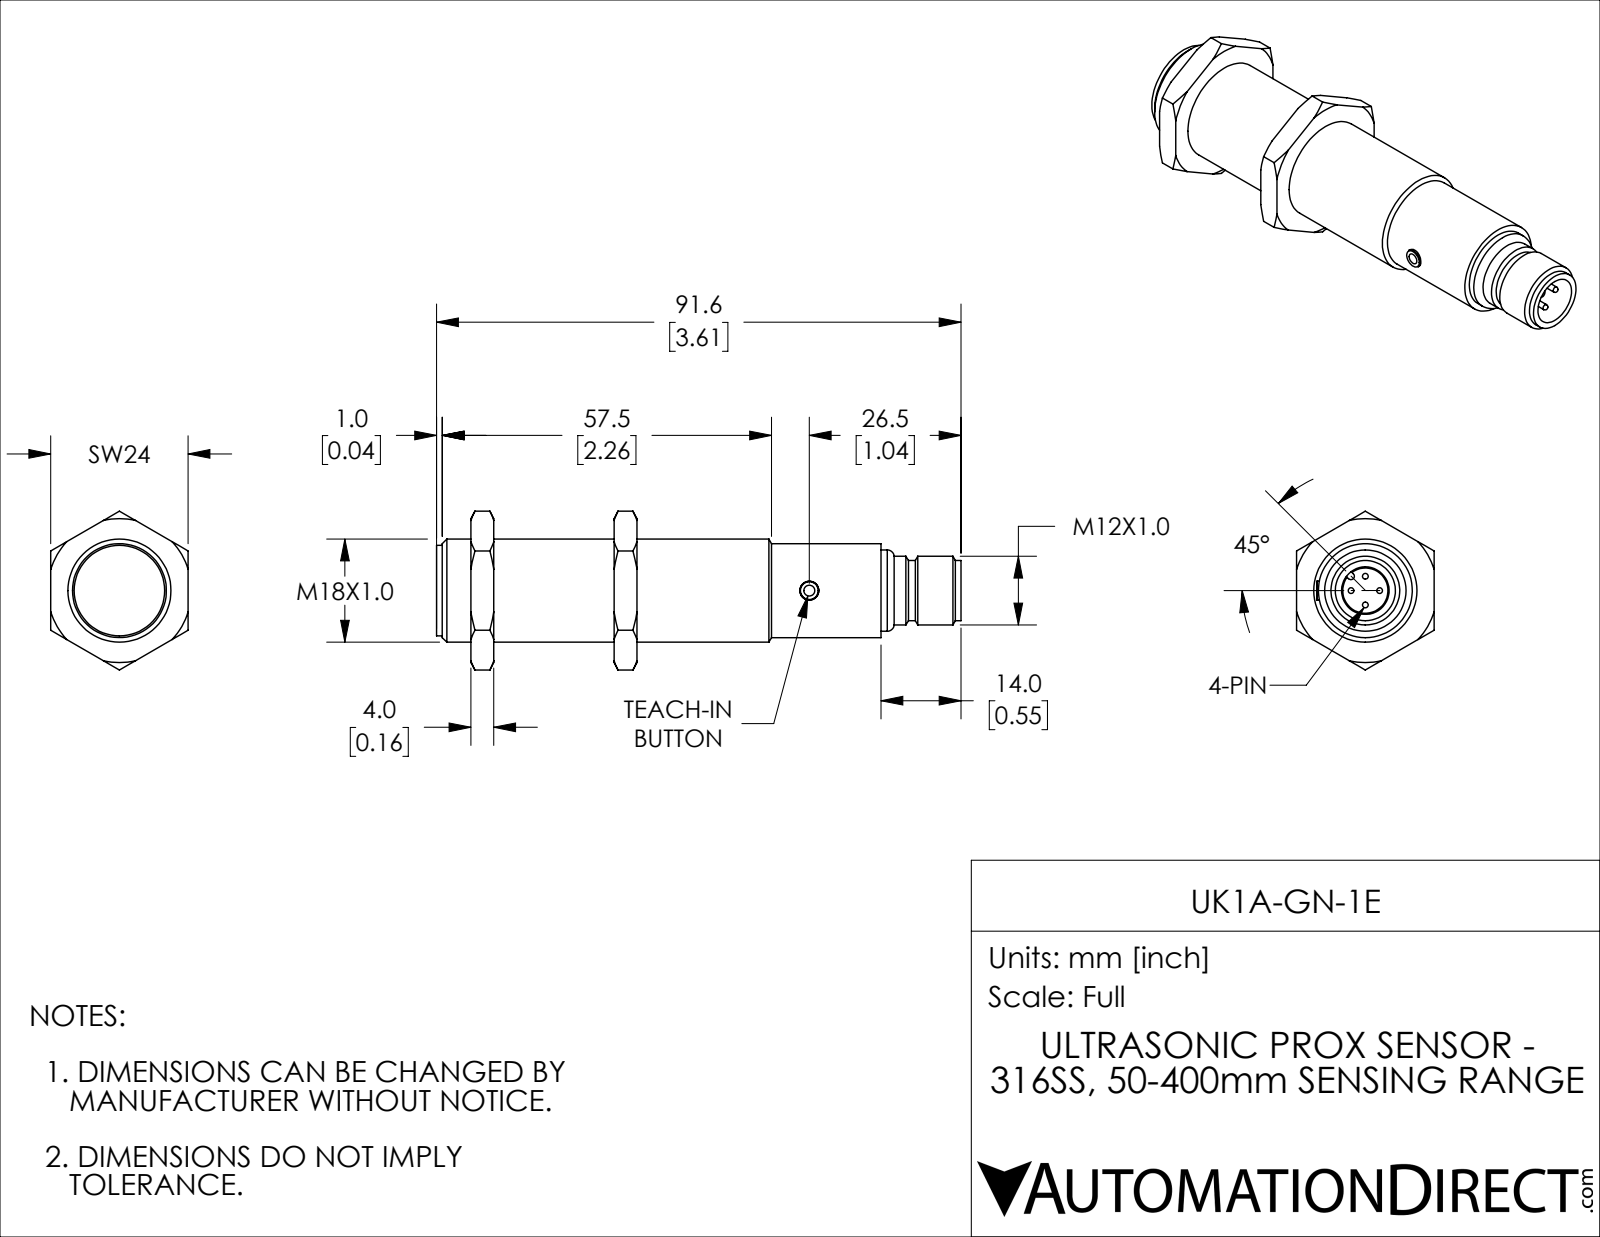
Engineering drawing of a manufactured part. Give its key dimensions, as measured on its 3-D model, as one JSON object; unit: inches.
{"part_name": "UK1A-GN-1E", "step_written_by": "SolidWorks 2018 (AUTOMOTIVE_DESIGN)", "units": "inches", "bodies": {"solids": 4, "faces": 113, "planar": 27, "cylindrical": 35, "other": 51}, "overall_size": [3.606, 1.091, 0.945], "volume_in3": 1.338, "surface_area_in2": 11.97, "round_holes": [[0.13, 1], [0.327, 1], [0.709, 1]], "round_bosses_or_shafts": [[0.039, 4], [0.646, 1], [0.622, 1], [0.559, 1], [0.472, 1], [0.413, 1]], "partial_cylinders_radius": [[0.024, 1]], "face_to_face_distances": [0.984, 0.157, 0.945, 1.142, 0.827, 0.236, 0.394, 1.22, 1.378, 3.055]}
